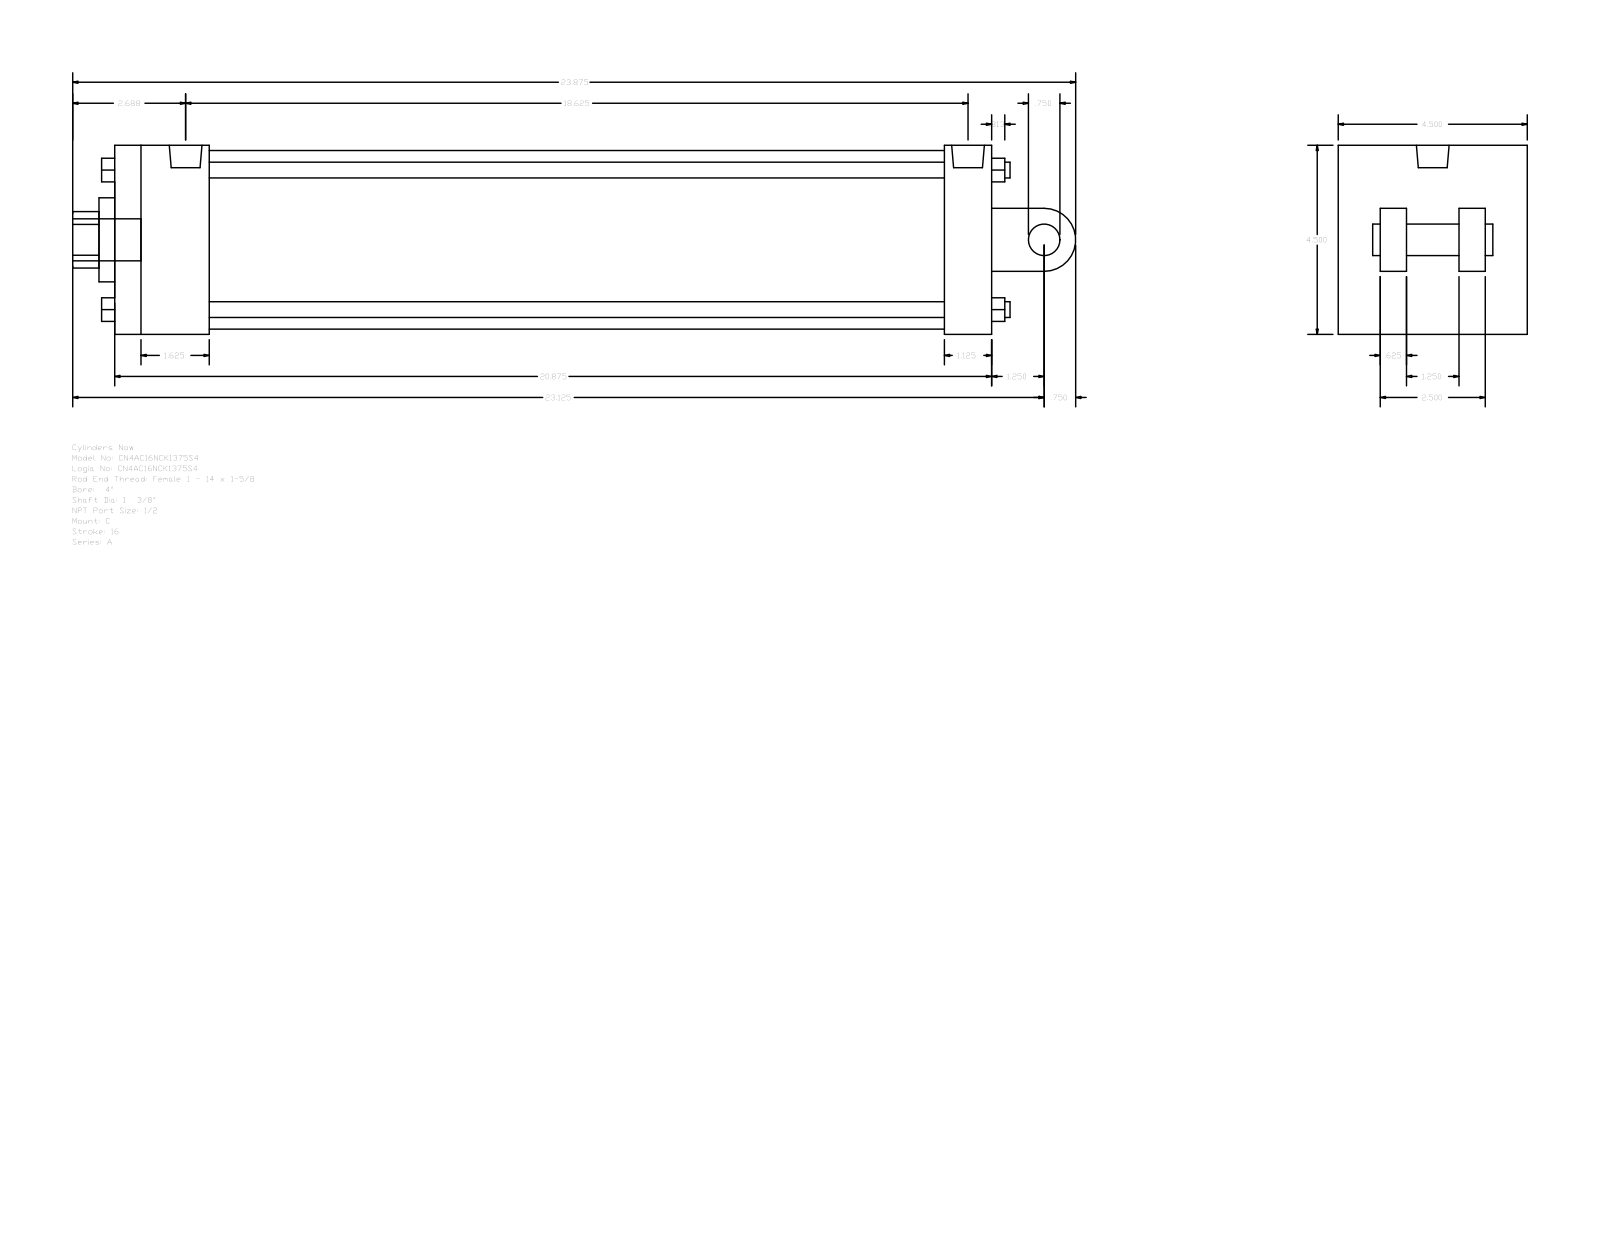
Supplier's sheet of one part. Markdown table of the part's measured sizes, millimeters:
| quantity | value |
| --- | --- |
| part name | A_C__0400_1.375 |
| STEP written by | GSSL Pune (CONFIG_CONTROL_DESIGN) |
| units | millimeters |
| bodies | 0 solids, 135 faces (102 planar, 33 cylindrical, 0 other) |
| overall size | 606.42 × 114.3 × 114.3 |
| round holes (diameter × count) | 8.73 × 2, 19.77 × 1, 34.92 × 1, 50.8 × 1, 107.95 × 1 |
| round bosses / shafts (diameter × count) | 9.53 × 4, 8.73 × 2, 25.4 × 1, 19.77 × 1, 19.05 × 1 |
| partial cylindrical surfaces (radius × count) | 17.06 × 1, 19.05 × 1 |
| main face-to-face distances | 114.3, 530.22, 73.03, 28.57, 501.65, 57.15, 444.5, 473.07, 15.87, 41.27 |
| hole center spacings | 3.18 |
